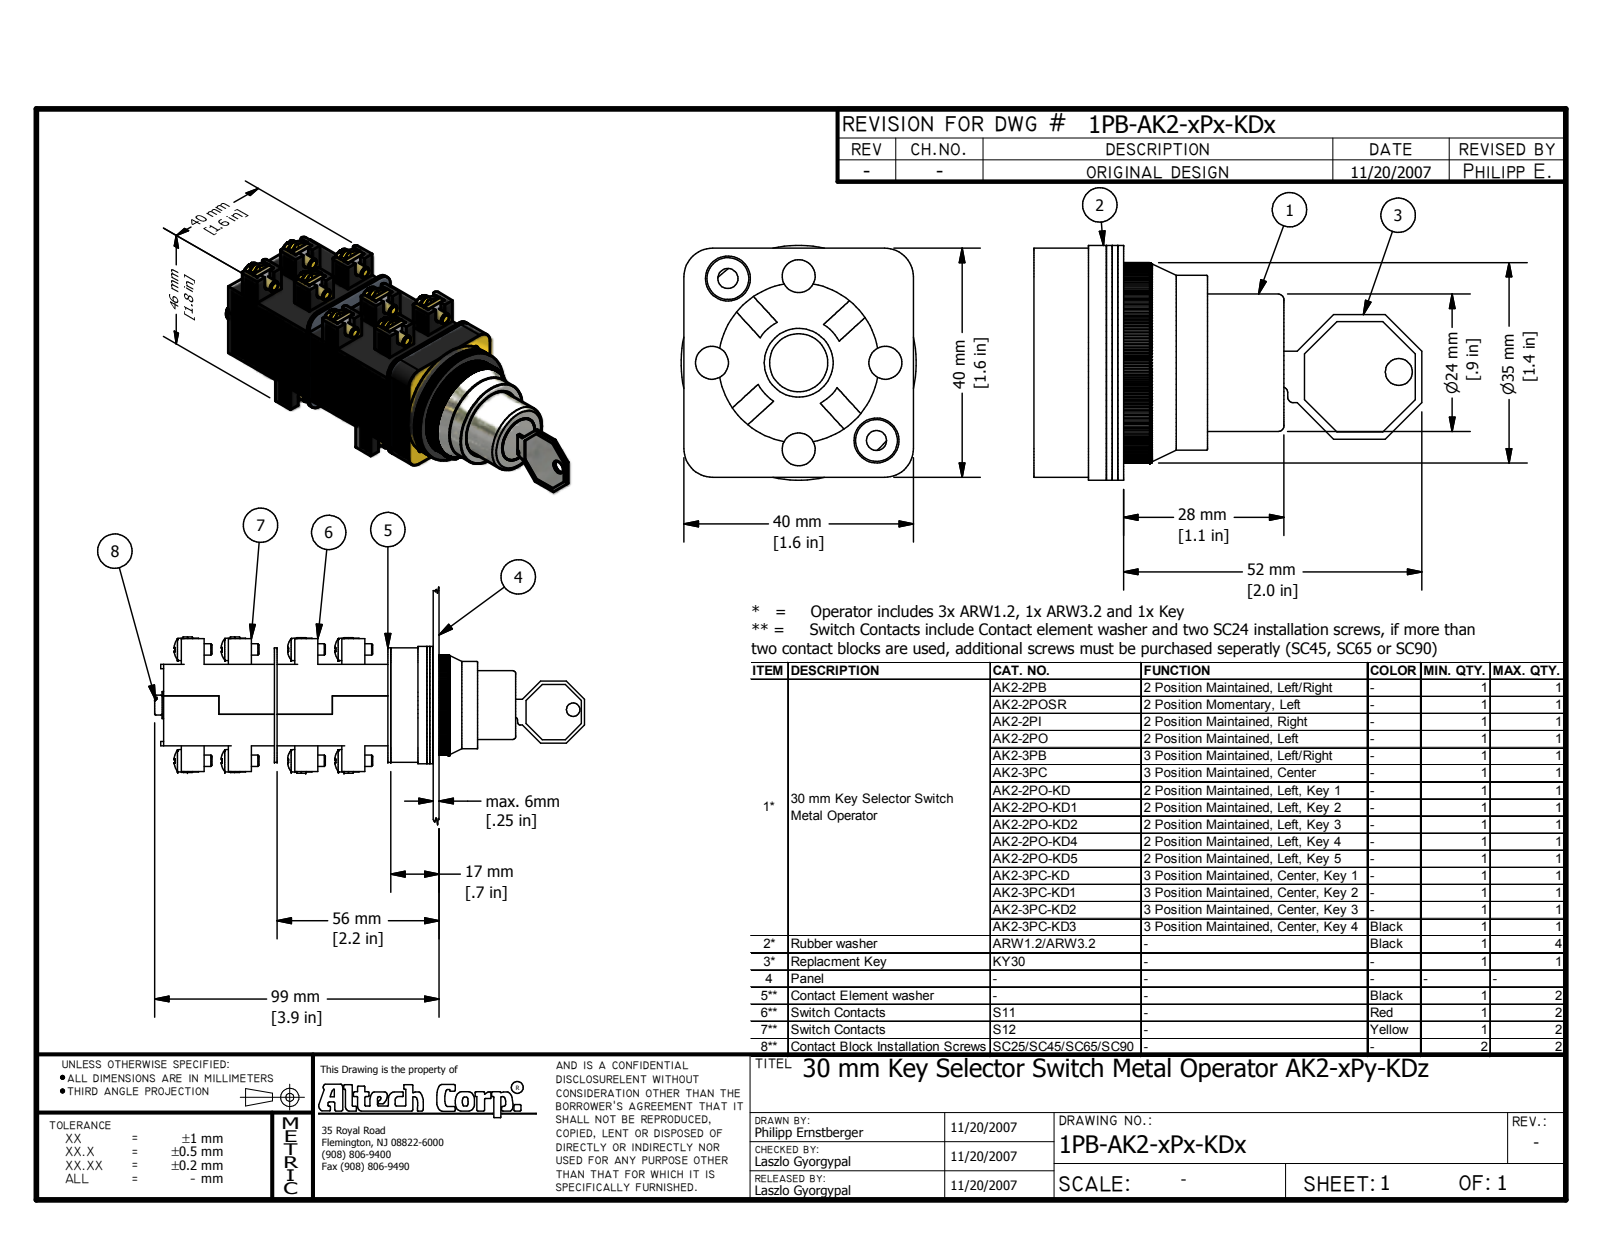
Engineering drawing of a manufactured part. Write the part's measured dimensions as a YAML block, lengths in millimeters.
part_name: "AK2-xPx-KDx; base; rubber_gasket_3mm; rubber_gasket_1mm (+2 more)"
step_written_by: "Autodesk Inventor 2008 (AUTOMOTIVE_DESIGN)"
units: millimeters
bodies: {solids: 7, faces: 761, planar: 493, cylindrical: 241, other: 27}
overall_size: [67.64, 41, 41]
volume: 38950
surface_area: 23223
round_holes:
  - {diameter: 5.75, count: 2}
  - {diameter: 3.5, count: 1}
  - {diameter: 7.85, count: 1}
  - {diameter: 12, count: 1}
  - {diameter: 16, count: 1}
  - {diameter: 24.5, count: 1}
  - {diameter: 25, count: 1}
  - {diameter: 27.5, count: 1}
  - {diameter: 30, count: 1}
  - {diameter: 30.5, count: 1}
  - {diameter: 31, count: 1}
round_bosses_or_shafts:
  - {diameter: 41, count: 1}
  - {diameter: 24, count: 1}
  - {diameter: 15.9, count: 1}
  - {diameter: 10.15, count: 1}
partial_cylinders:
  - {radius: 5, count: 4}
  - {radius: 1, count: 2}
  - {radius: 2, count: 2}
  - {radius: 14, count: 1}
  - {radius: 17.5, count: 1}
face_to_face_distances: [1, 2, 13.65, 3.15, 5.15, 4.15, 12.65, 14.65, 9.5, 20.5]
hole_center_spacings: [15.13, 14.96, 19.19, 21.4, 32.28]
